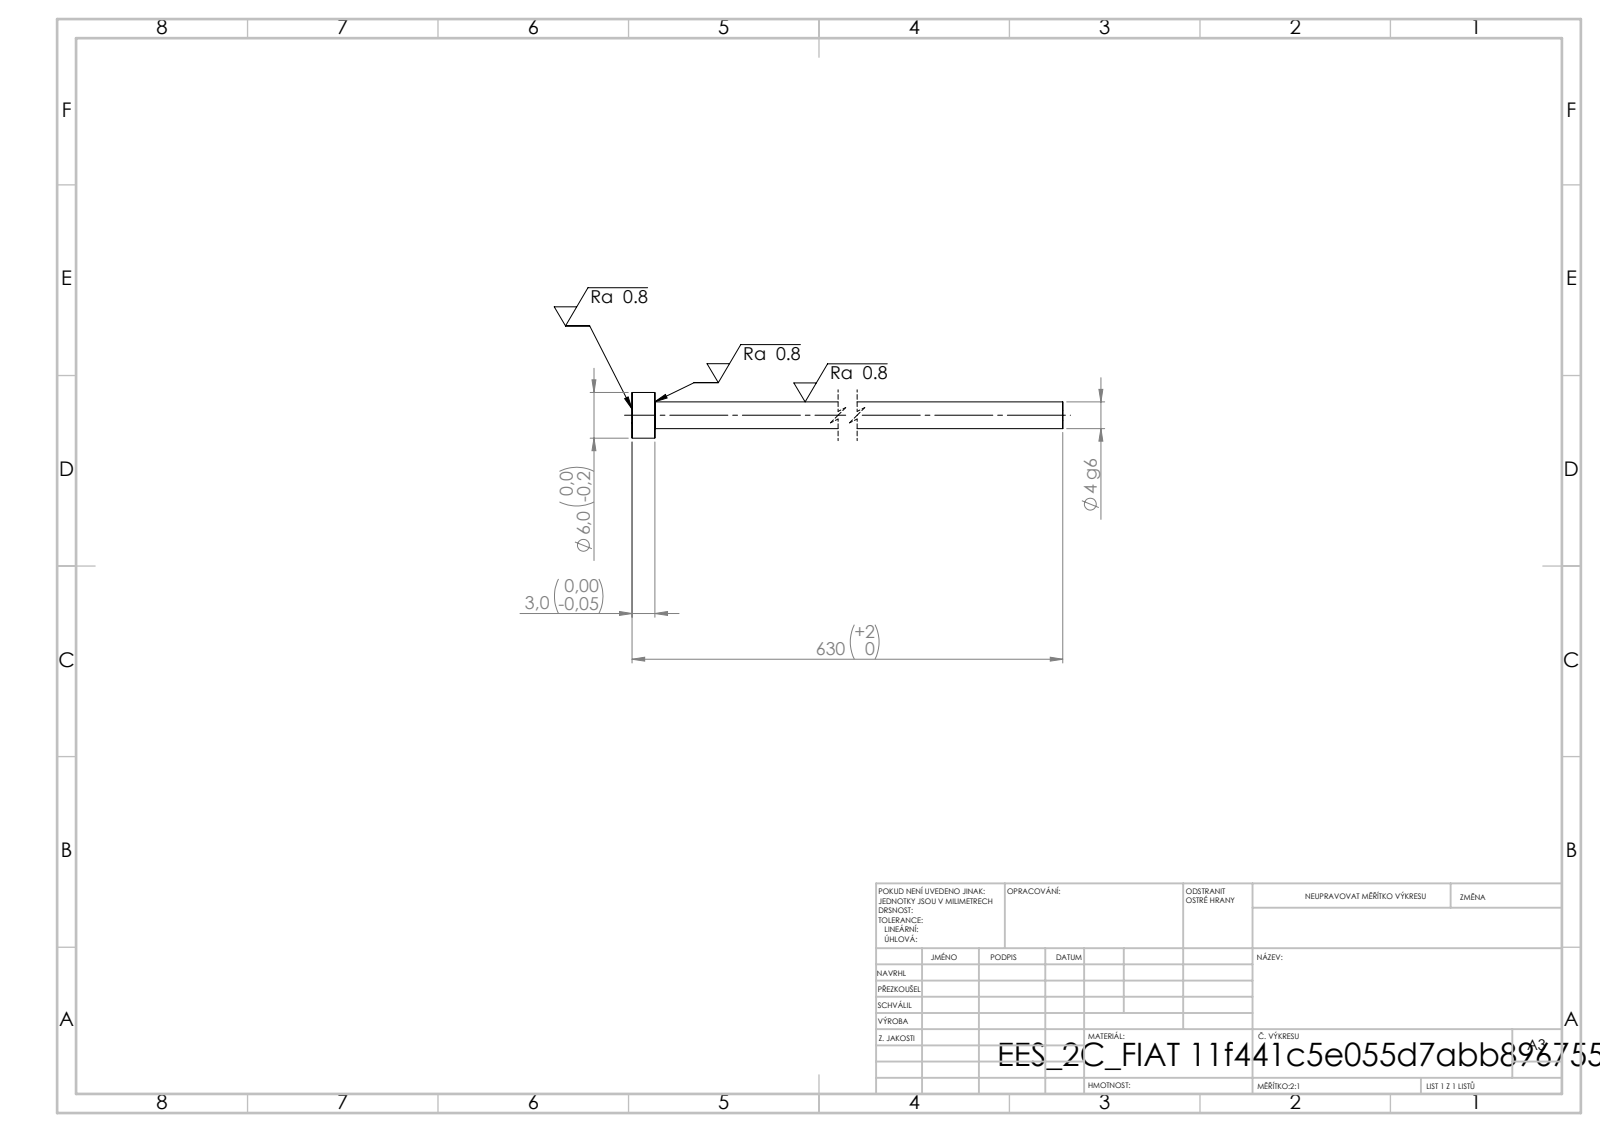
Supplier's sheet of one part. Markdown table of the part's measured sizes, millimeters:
| quantity | value |
| --- | --- |
| STEP written by | SolidWorks 2019 (CONFIG_CONTROL_DESIGN) |
| units | millimeters |
| bodies | 1 solid, 7 faces (3 planar, 4 cylindrical, 0 other) |
| overall size | 630 × 6 × 6 |
| volume | 6 117 mm³ |
| surface area | 7 007 mm² |
| round bosses / shafts (diameter × count) | 6 × 1, 3.5 × 1 |
| main face-to-face distances | 3, 630, 627 |
